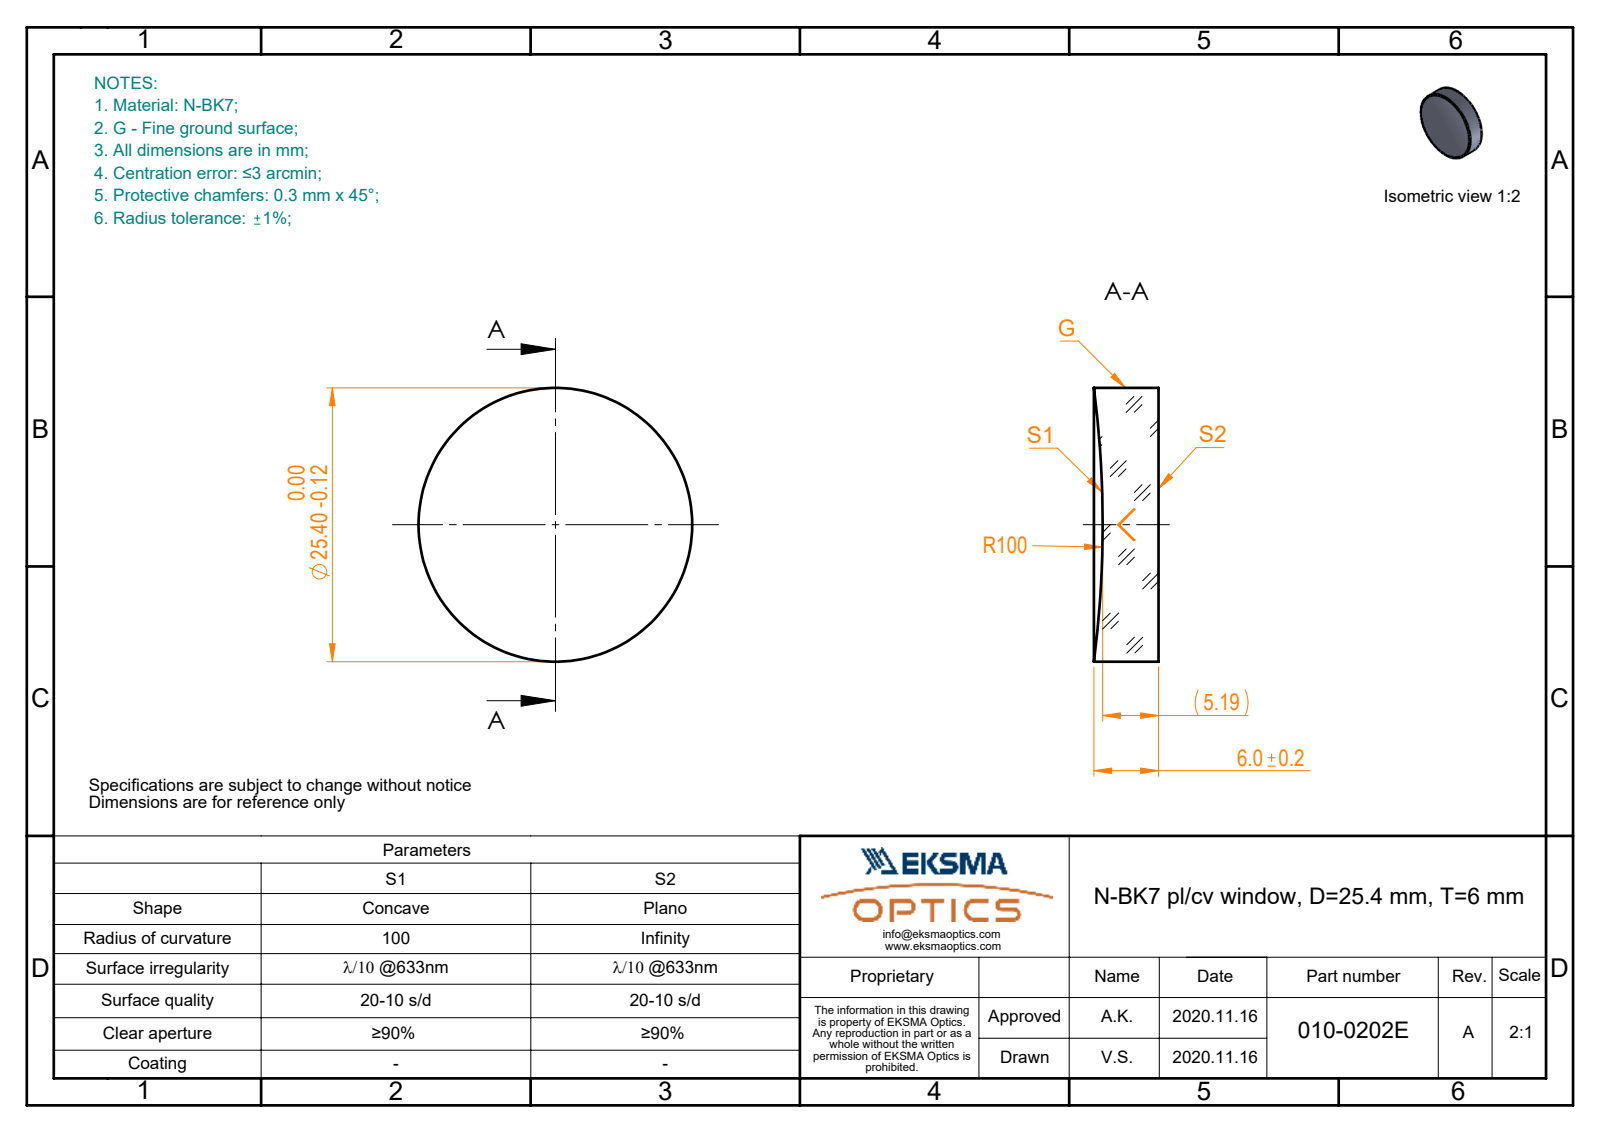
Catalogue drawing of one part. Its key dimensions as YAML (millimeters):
part_name: "010-0202E_N-BK7_PCV_mirror"
step_written_by: "SolidWorks 2019 (CONFIG_CONTROL_DESIGN)"
units: millimeters
bodies: {solids: 1, faces: 5, planar: 1, cylindrical: 2, other: 2}
overall_size: [25.4, 25.4, 6]
volume: 2835
surface_area: 1494
round_bosses_or_shafts:
  - {diameter: 25.4, count: 1}
